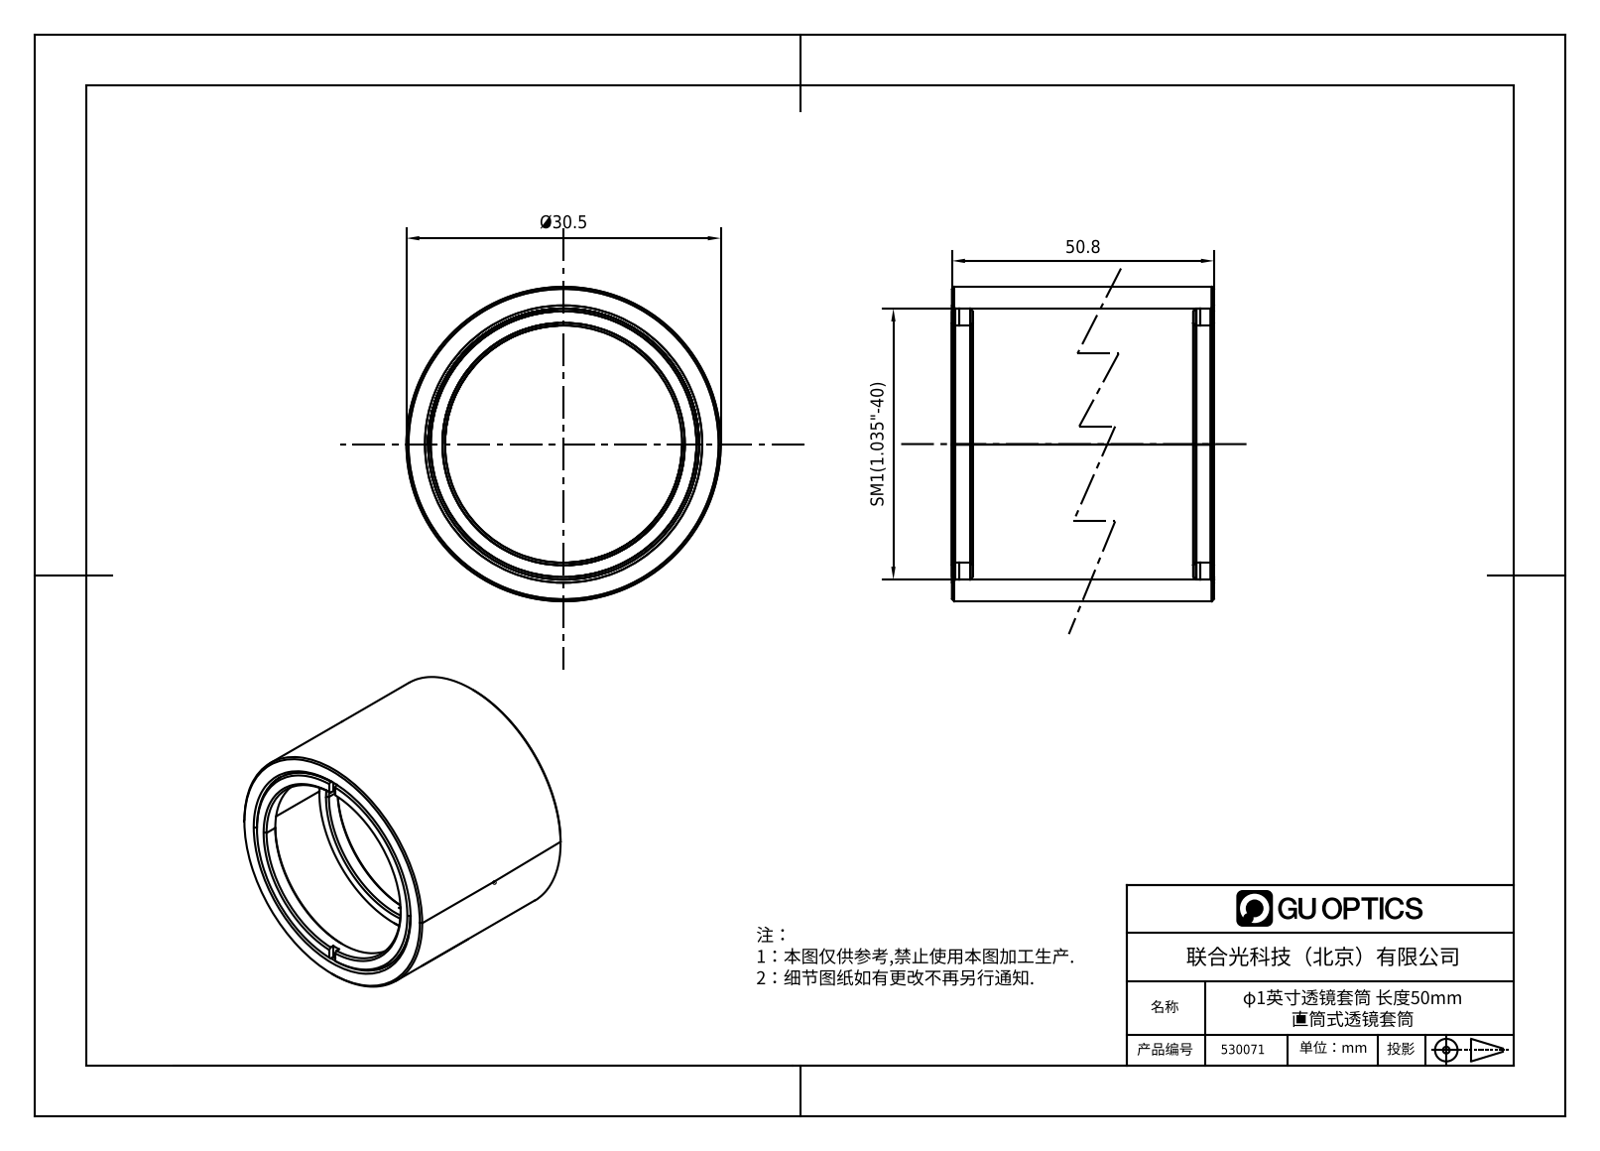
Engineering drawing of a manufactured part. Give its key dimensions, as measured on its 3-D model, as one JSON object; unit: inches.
{"part_name": "1.7.2.10_ZTZ-1-2.0_SM1标准型2.0英寸直筒式透镜套筒", "step_written_by": "SolidWorks 2018 (AUTOMOTIVE_DESIGN)", "units": "inches", "bodies": {"solids": 0, "faces": 54, "planar": 18, "cylindrical": 12, "other": 24}, "overall_size": [2, 1.201, 1.201], "round_holes": [[0.906, 1], [1.035, 1]], "round_bosses_or_shafts": [[1.201, 1], [1.035, 1]], "face_to_face_distances": [2, 0.028, 1.972, 0.039, 1.945]}
